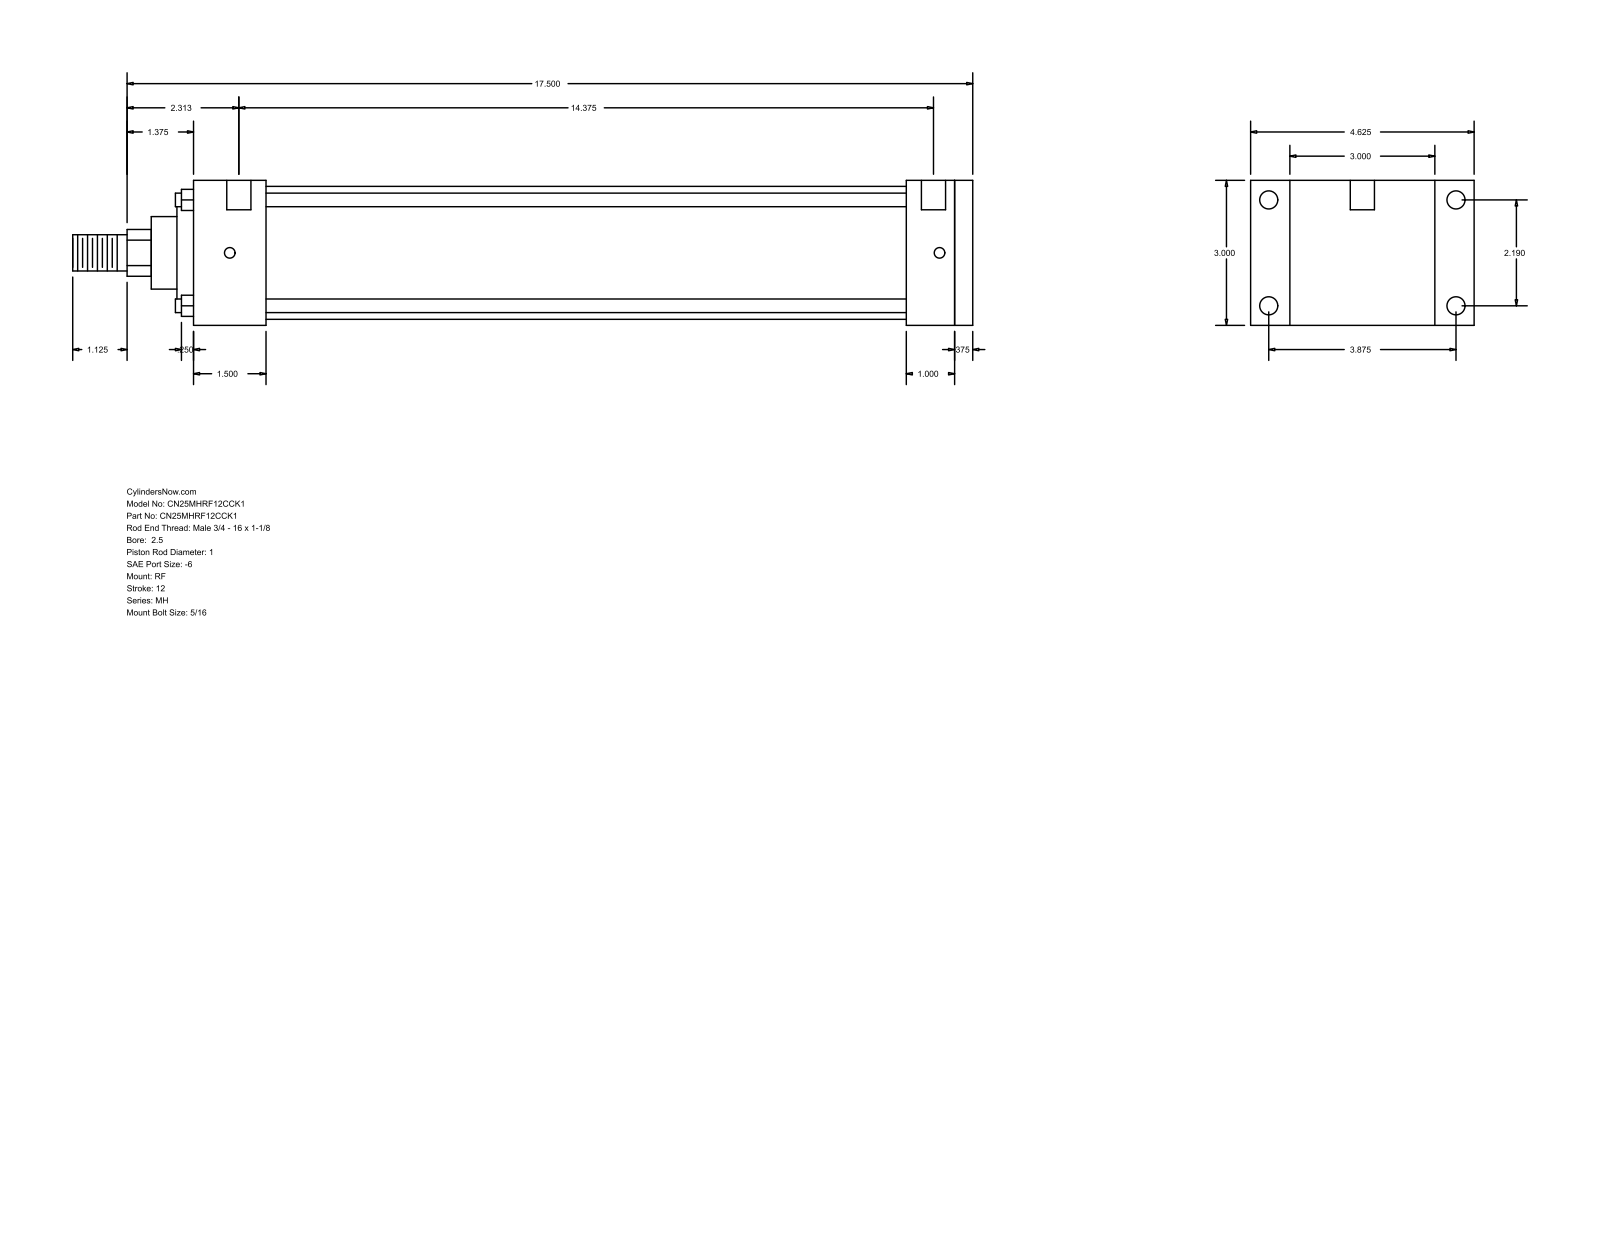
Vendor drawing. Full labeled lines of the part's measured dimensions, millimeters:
Part name (STEP PRODUCT): MH_RF__0250_1
STEP written by: GSSL Pune (CONFIG_CONTROL_DESIGN)
Units: millimetres
Bodies: 0 solids, 94 faces (65 planar, 29 cylindrical, 0 other)
Overall size (bounding box): 473.07 × 117.47 × 76.2
Round holes (diameter × count): ⌀5.56 ×4, ⌀9.53 ×4, ⌀12.7 ×2
Round bosses / shafts (diameter × count): ⌀7.14 ×4, ⌀69.85 ×1, ⌀60.33 ×1, ⌀38.1 ×1, ⌀25.4 ×1, ⌀19.05 ×1
Partial cylindrical surfaces — rounded edges, fillets, slot ends (radius × count): R12.29 ×1
Main face-to-face distances: 76.2, 9.52, 409.58, 400.06, 374.65, 25.41, 34.93, 38.11, 336.54, 361.95
Hole centre spacings: 55.62, 98.42, 113.05, 373.06, 3.18, 4.76, 365.12, 368.3
